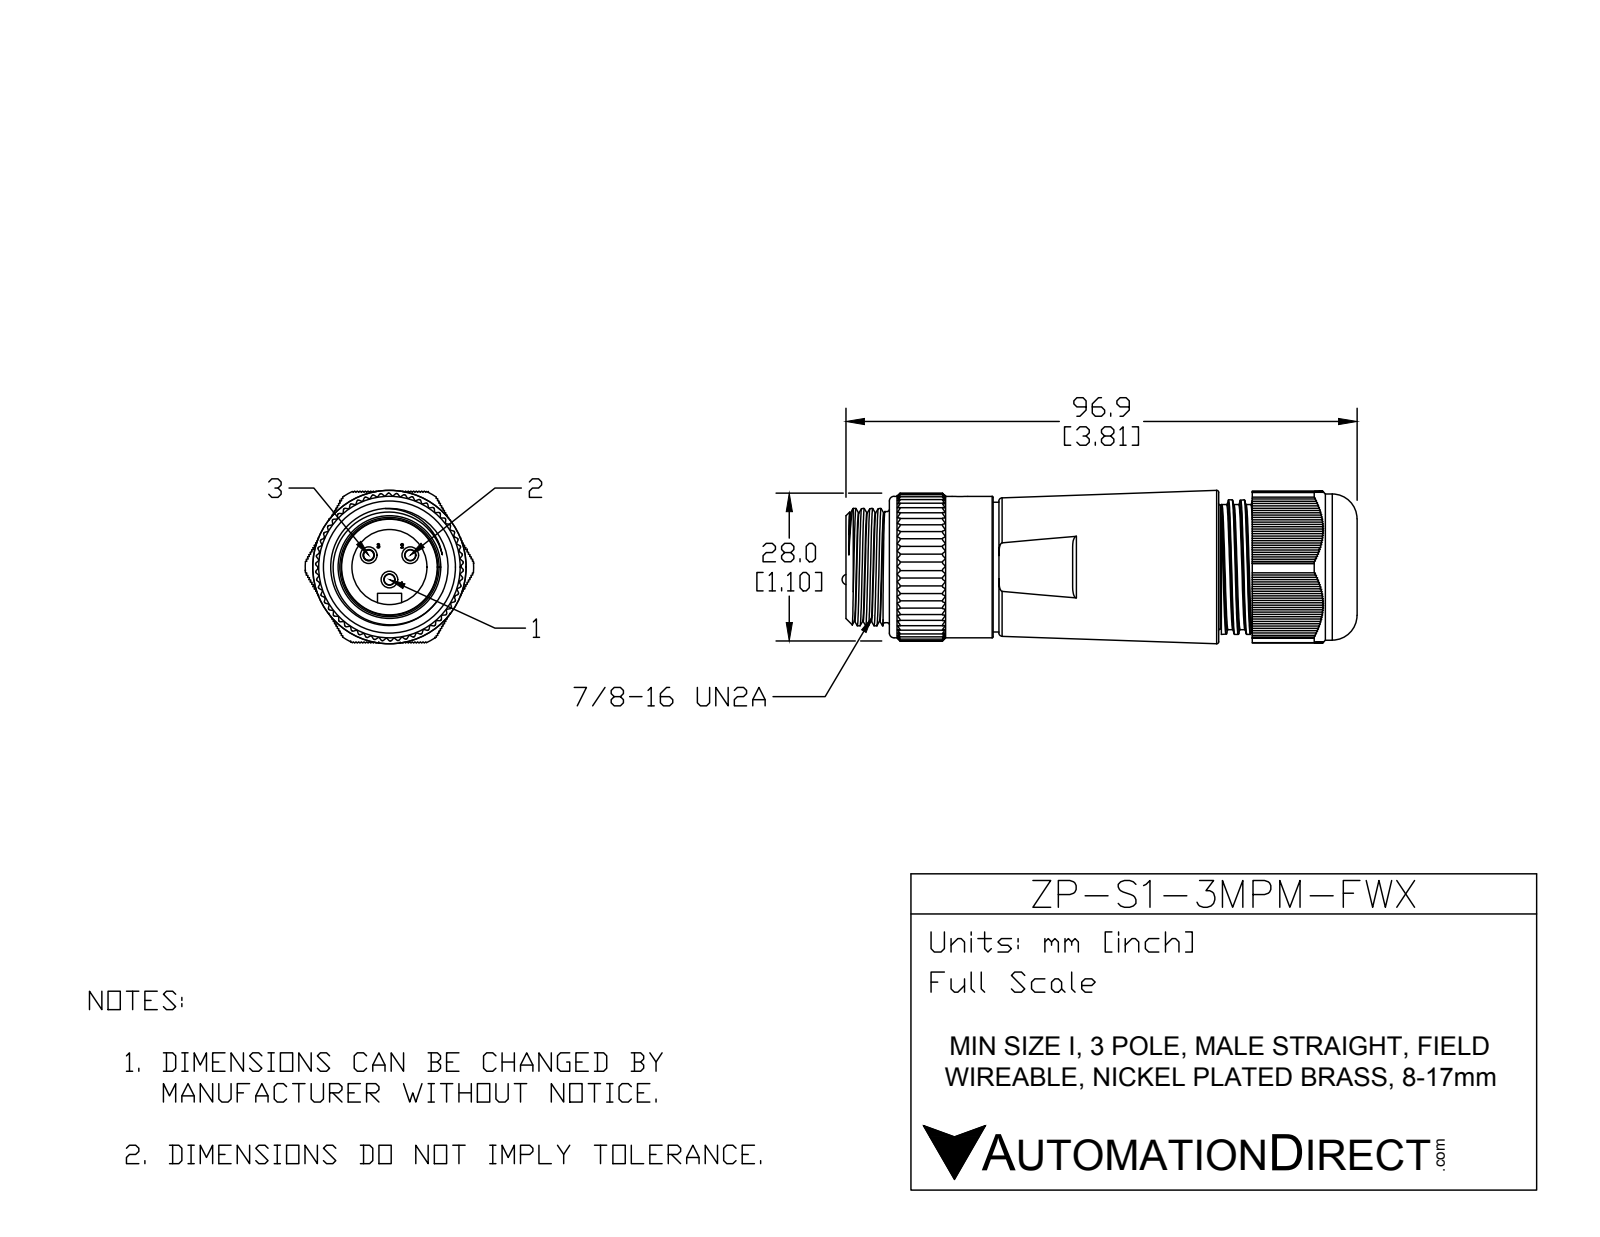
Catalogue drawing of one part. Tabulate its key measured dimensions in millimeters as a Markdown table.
| quantity | value |
| --- | --- |
| part name | MIN-3MPM-FWX |
| STEP written by | SolidWorks 2015 (AUTOMOTIVE_DESIGN) |
| units | millimeters |
| bodies | 1 solid, 1098 faces (673 planar, 346 cylindrical, 79 other) |
| overall size | 97.56 × 31.9 × 29.06 |
| volume | 53 593 mm³ |
| surface area | 16 107 mm² |
| round holes (diameter × count) | 3.5 × 1, 14.22 × 1, 17.27 × 1, 18.29 × 1, 24.13 × 1, 25.4 × 1 |
| round bosses / shafts (diameter × count) | 3.15 × 3, 2 × 3, 27.69 × 1, 26.8 × 1, 25.5 × 1, 24.56 × 1, 24 × 1, 22.23 × 1 |
| partial cylindrical surfaces (radius × count) | 0.25 × 116, 0.2 × 58, 2.29 × 1, 14 × 1, 15.95 × 1 |
| main face-to-face distances | 0.36, 0.72, 1.08, 6.35, 69.77, 18.74, 19.16, 1.44, 25.09, 1.8 |
